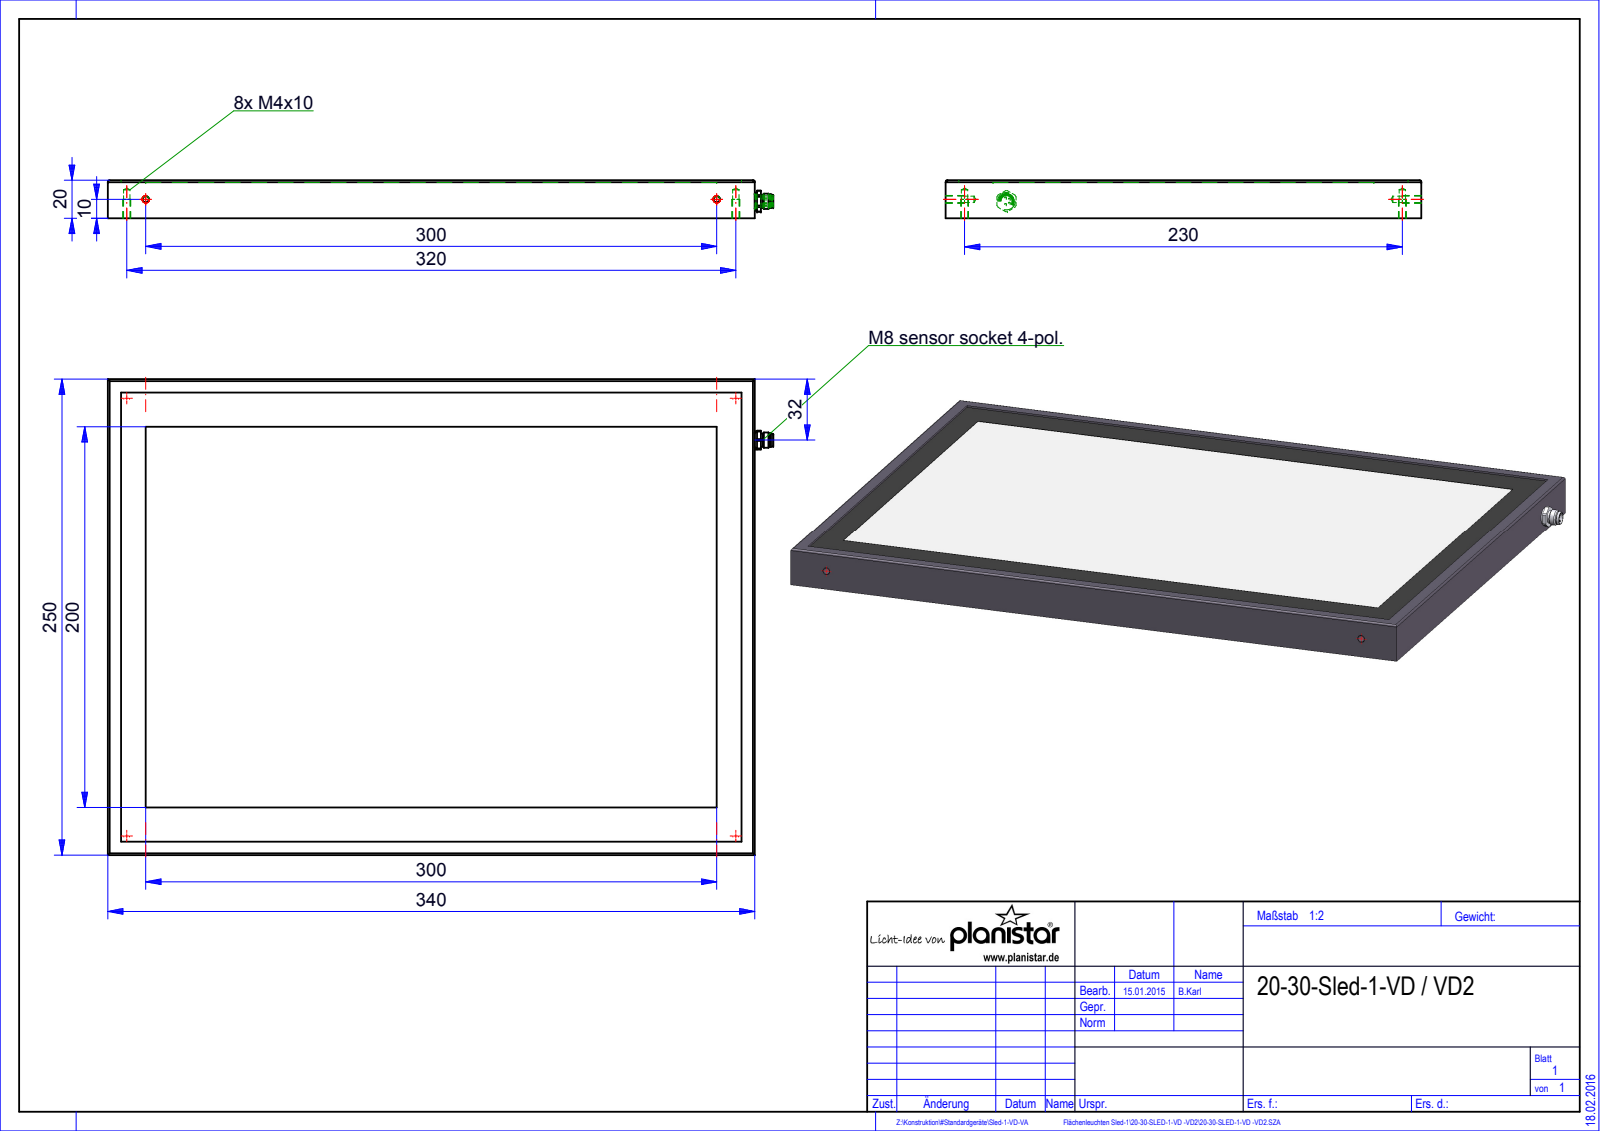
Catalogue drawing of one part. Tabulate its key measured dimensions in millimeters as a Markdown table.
| quantity | value |
| --- | --- |
| part name | Root; Baugruppe_Xled-2-VD; QUADER_0; 09-3391-00-04 |
| STEP written by | HiCAD 2015 2002.1 Build 408 (AUTOMOTIVE_DESIGN) |
| units | millimeters |
| bodies | 2 solids, 90 faces (36 planar, 37 cylindrical, 17 other) |
| overall size | 349.7 × 250 × 20 |
| volume | 1 610 000 mm³ |
| surface area | 196 477 mm² |
| round holes (diameter × count) | 3.3 × 6, 4 × 6, 5.8 × 1 |
| round bosses / shafts (diameter × count) | 1 × 4, 8 × 1, 7.2 × 1, 6.8 × 1, 6.4 × 1 |
| partial cylindrical surfaces (radius × count) | 1 × 4, 5.5 × 1 |
| main face-to-face distances | 18.8, 19, 20, 1.2, 1, 250, 340, 7, 243, 333 |
| hole center spacings | 230, 320, 394.08, 300 |
